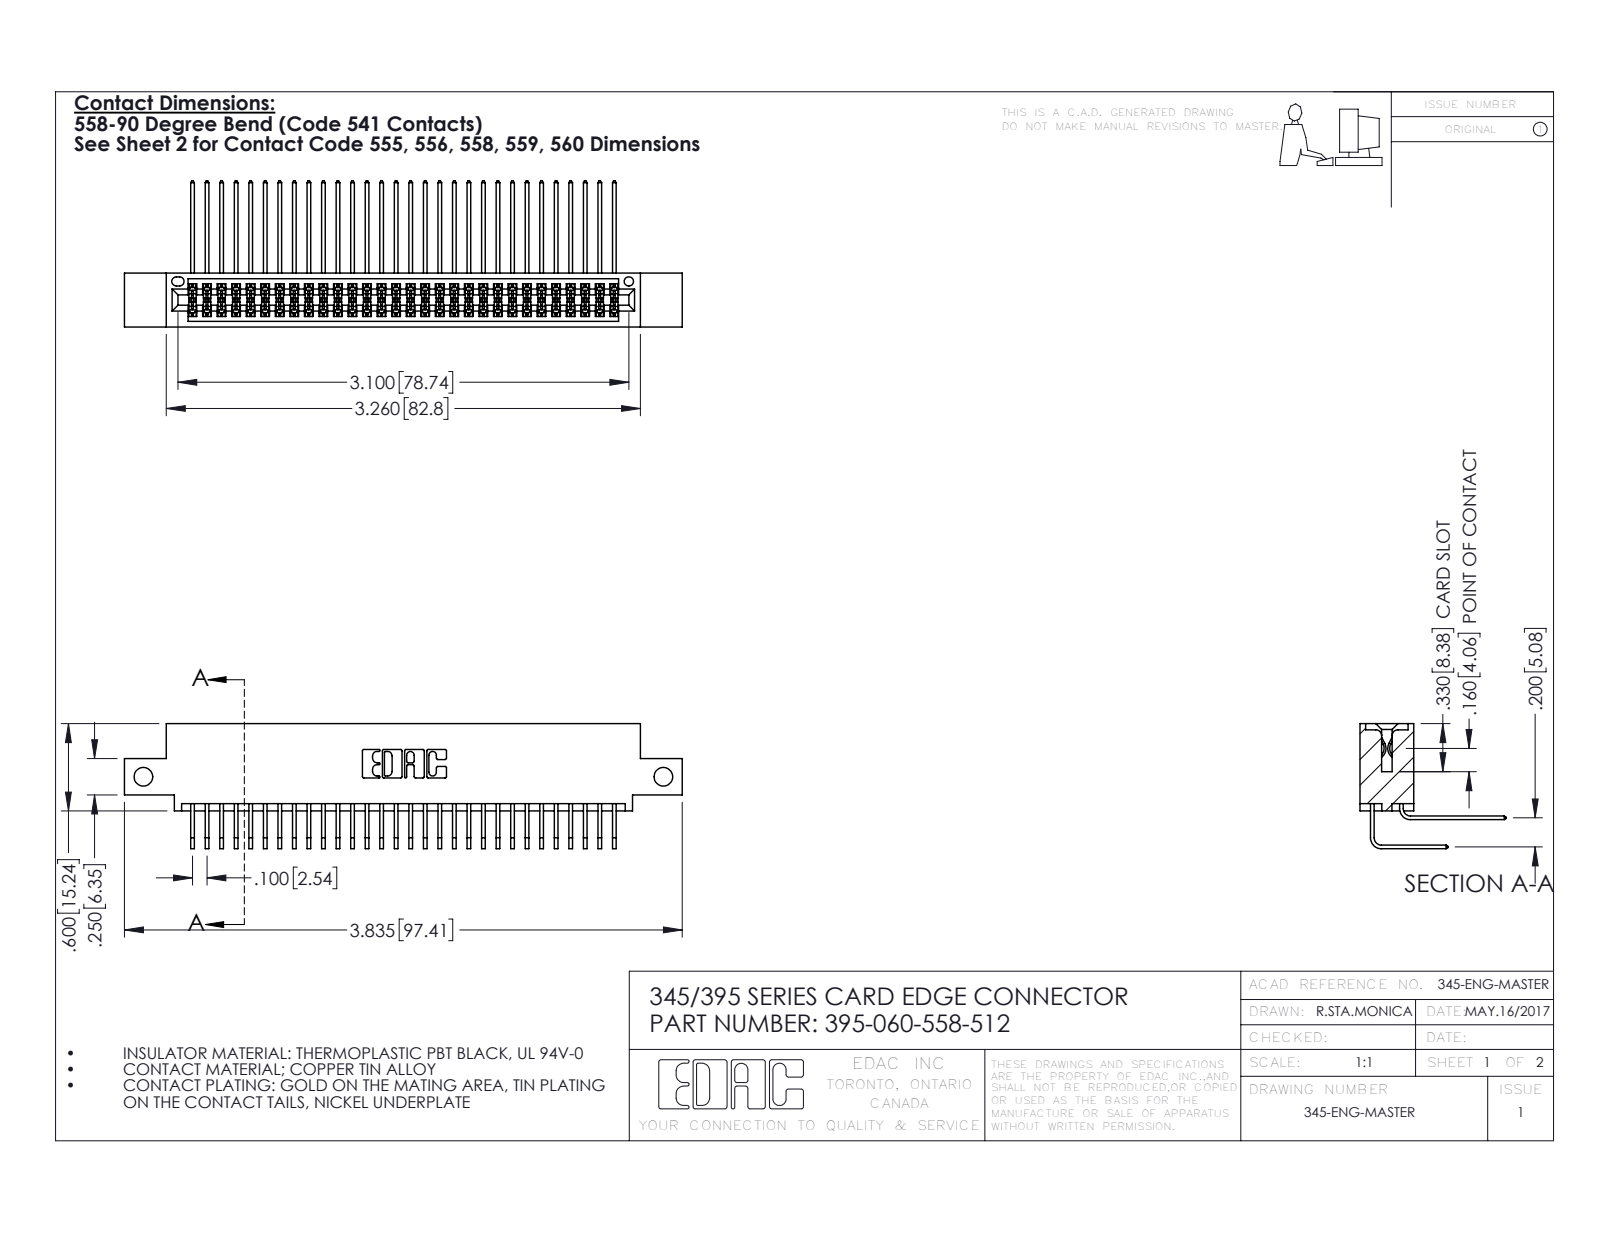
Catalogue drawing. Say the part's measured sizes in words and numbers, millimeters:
The part is named "345 Part_0.110 Offset - Side Mount; 345-292-001_558 559 Tail - 1; 345-292-001_558 Tail - 2; 395-060-558-512". Its 3-D file was written by "SolidWorks 2016 (CONFIG_CONTROL_DESIGN)". It is 61 solids with 3250 faces: 2184 planar, 1066 cylindrical and 0 other. Overall it measures 97.4 by 25.5 by 21.8 millimeters. Its volume is 9 540 cubic millimeters and its surface area 15 450 square millimeters. Round holes: 2 of diameter 3.3, 1 of diameter 1.6. Partial cylindrical surfaces (rounded edges, fillets, slot ends): 91 of radius 0.2, 22 of radius 0.3, 6 of radius 0.2, 6 of radius 0.8, 3 of radius 0.7, 2 of radius 0.4, 2 of radius 0.5, 2 of radius 0.6. The main face-to-face distances are 1.8, 7.6, 5.1, 9.4, 2.5, 6.9, 0.6, 5.7, 0.6, 4.4. The hole center spacings are 90.8.
